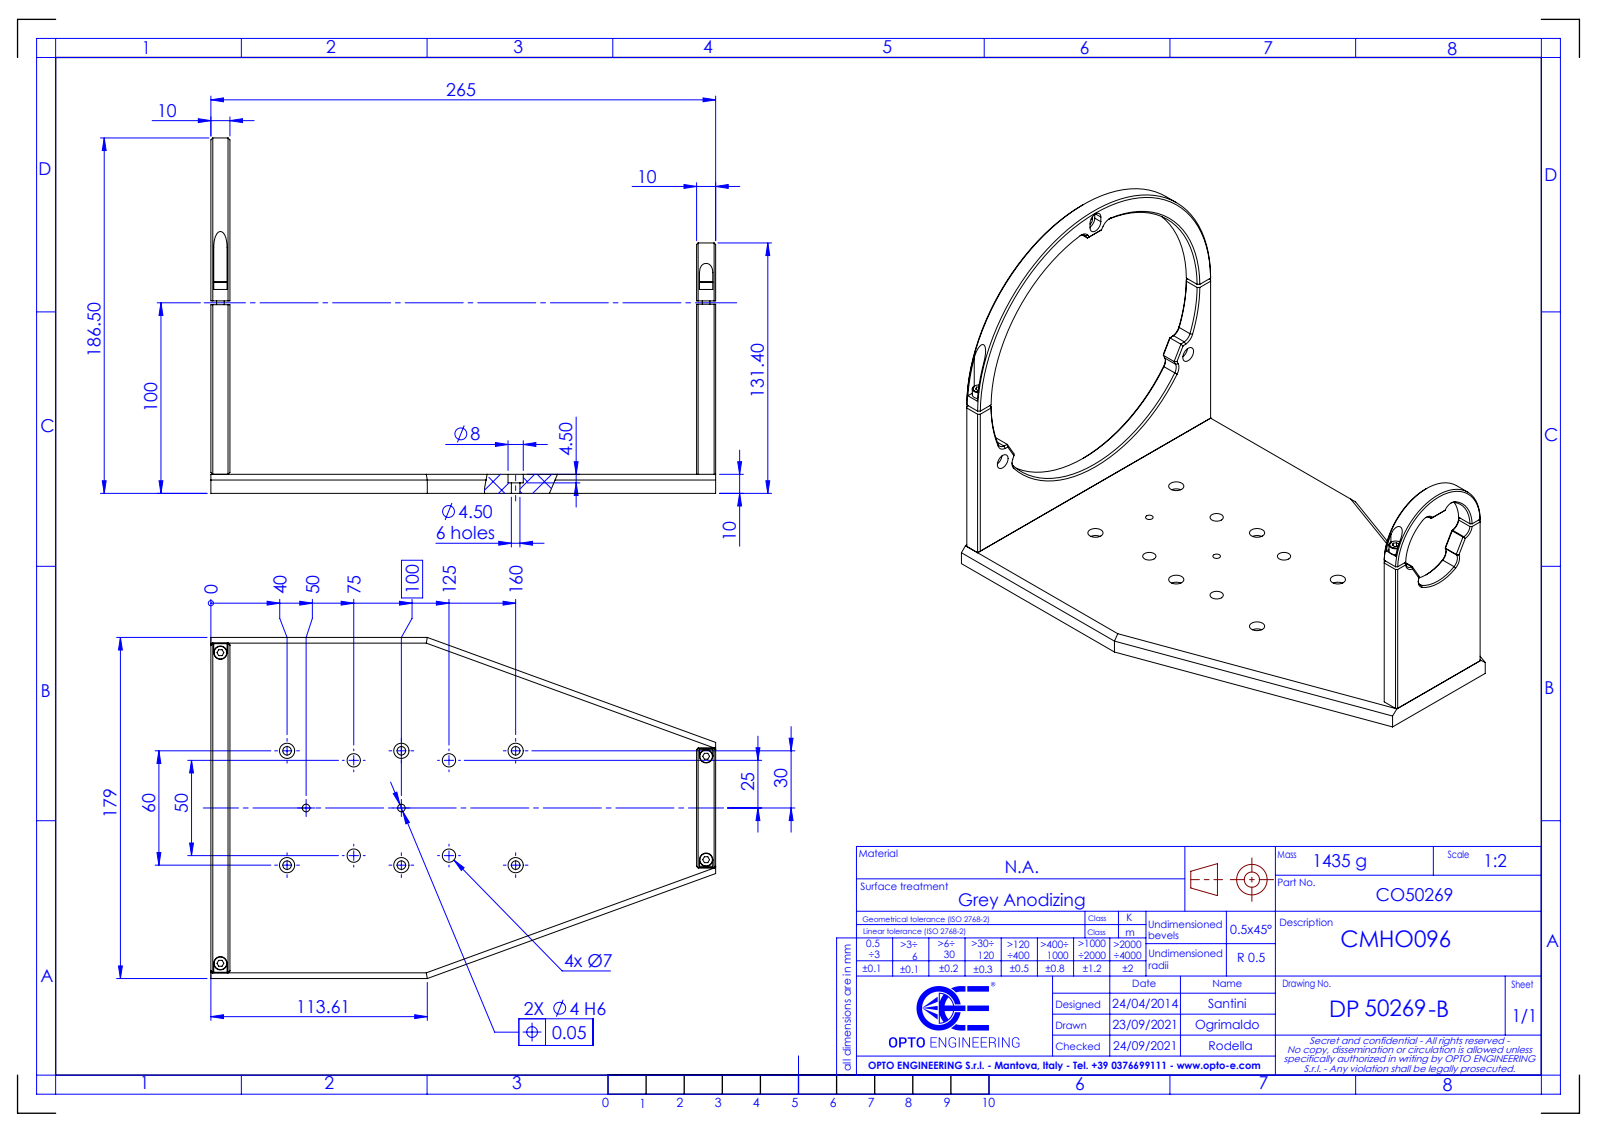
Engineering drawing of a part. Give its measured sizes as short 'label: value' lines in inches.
name: DP50269-B_CMHO096
written by: SolidWorks 2021 (CONFIG_CONTROL_DESIGN)
unit: in
bodies: 0 solids, 316 faces (154 planar, 98 cylindrical, 64 other)
size: 10.433 × 7.343 × 7.047
holes: 12× ⌀0.315, 8× ⌀0.177, 6× ⌀0.276, 2× ⌀0.157, 1× ⌀6.024
bosses: 2× ⌀0.276, 2× ⌀0.157
rounds: 12× R0.197, 2× R0.089, 2× R0.157, 1× R0.941, 1× R1.236, 1× R3.406
face distances: 0.394, 10.039, 10.433, 9.646, 0.118, 2.287, 4.76, 6.929, 2.169, 4.642
hole spacings: 1.392, 2.362, 1.969, 1.004, 2.379, 2.567, 2.641, 3.341
